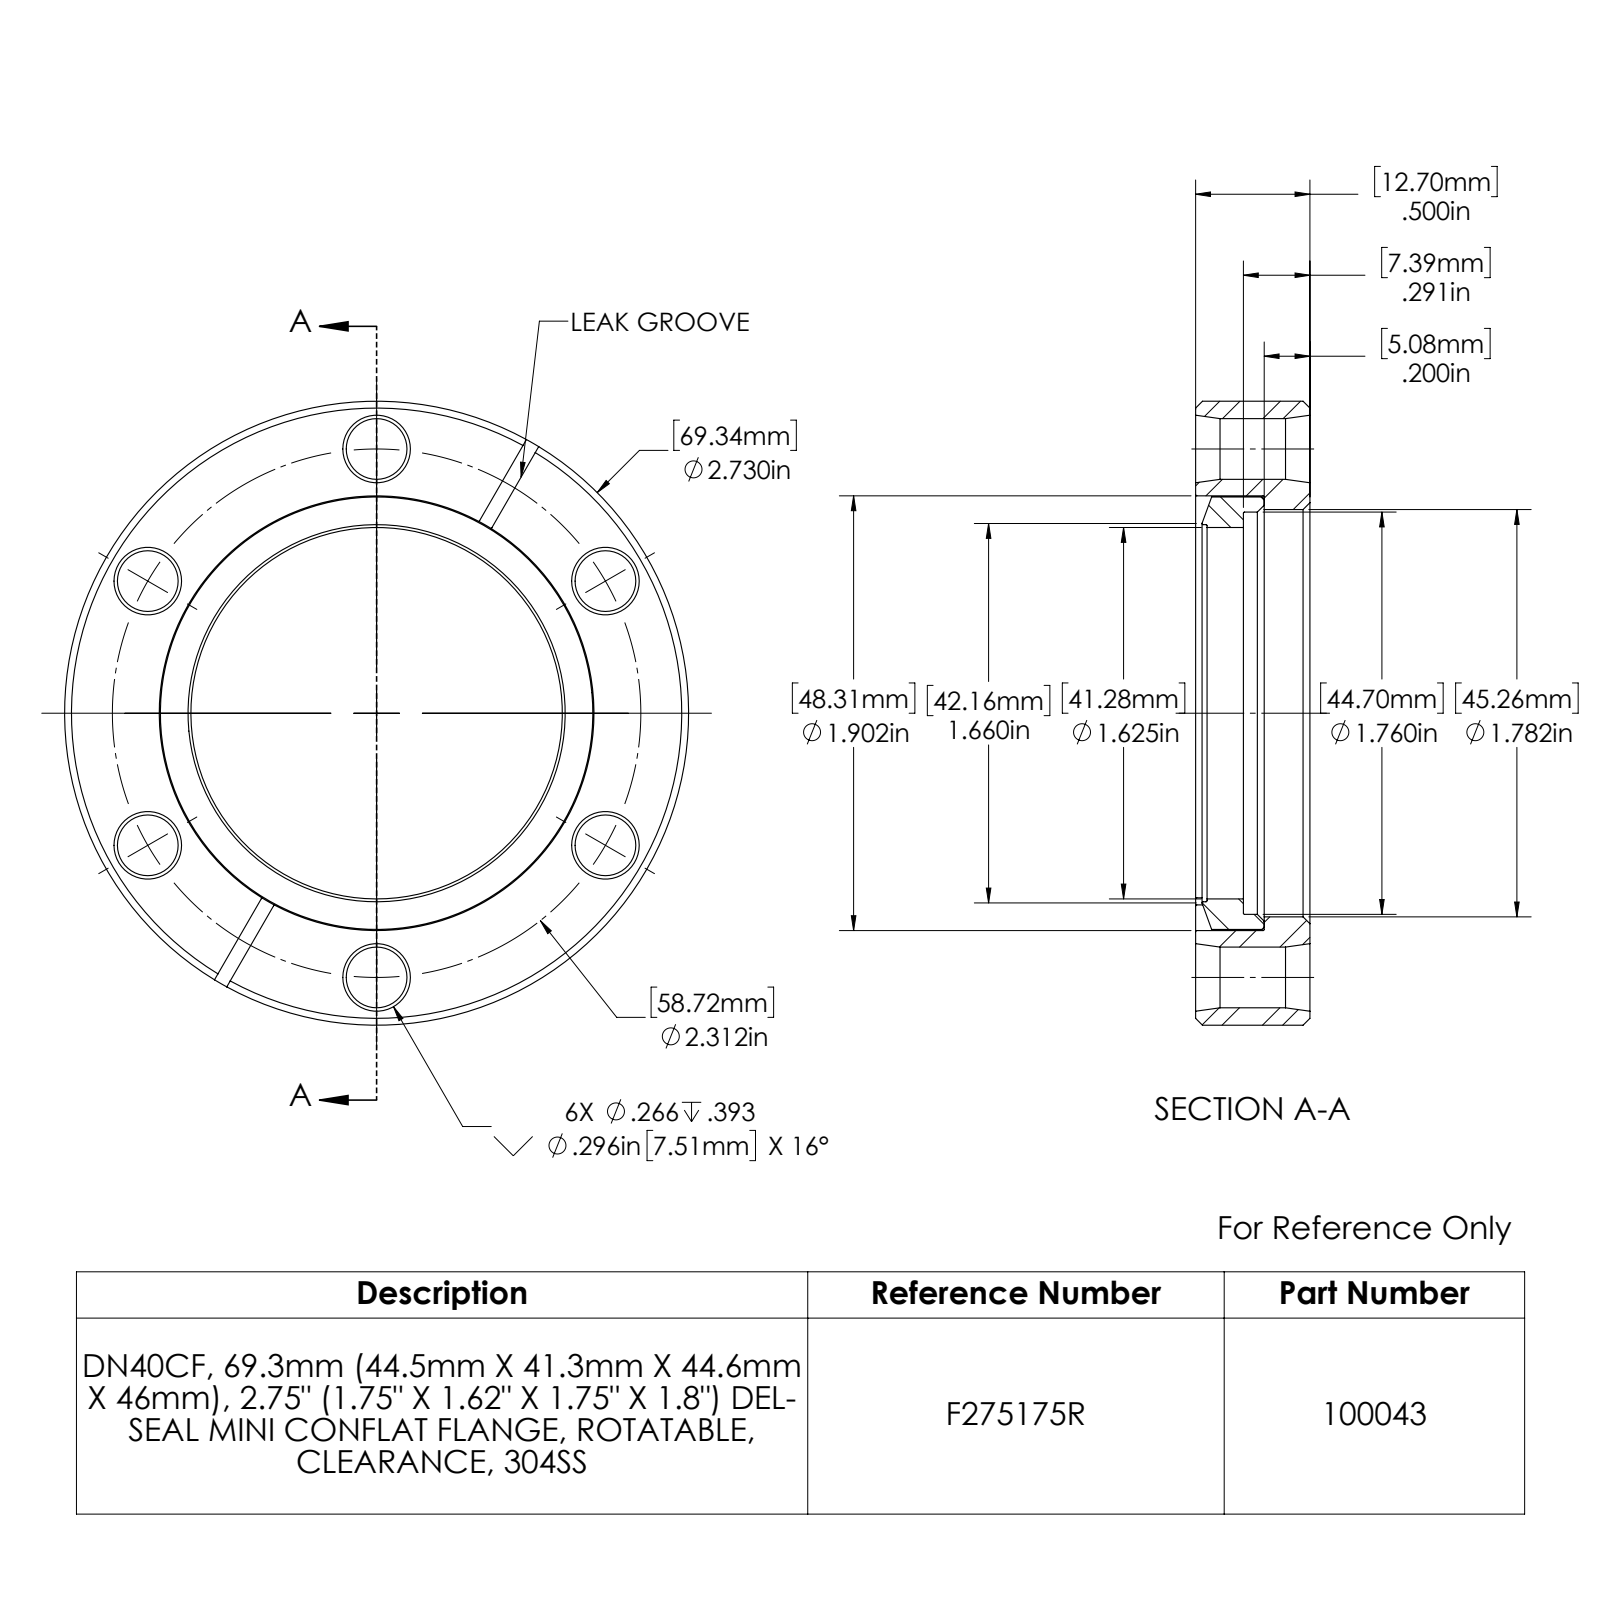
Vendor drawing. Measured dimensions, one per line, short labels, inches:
name: 990363; 990367; 100043_A
written by: SolidWorks 2022 (CONFIG_CONTROL_DESIGN)
unit: in
bodies: 2 solids, 87 faces (13 planar, 26 cylindrical, 48 other)
size: 2.73 × 2.73 × 0.5
volume: 1.538 in³; area: 19.48 in²
holes: 6× ⌀0.266, 1× ⌀1.625, 1× ⌀1.65, 1× ⌀1.76, 1× ⌀1.782, 1× ⌀1.902
bosses: 1× ⌀2.73, 1× ⌀1.892
face distances: 0.5, 0.3, 0.2, 0.209, 0.091, 0.291, 0.062, 0.147, 0.238, 0.438
hole spacings: 1.156, 2.002, 2.002, 2.312, 2.312
